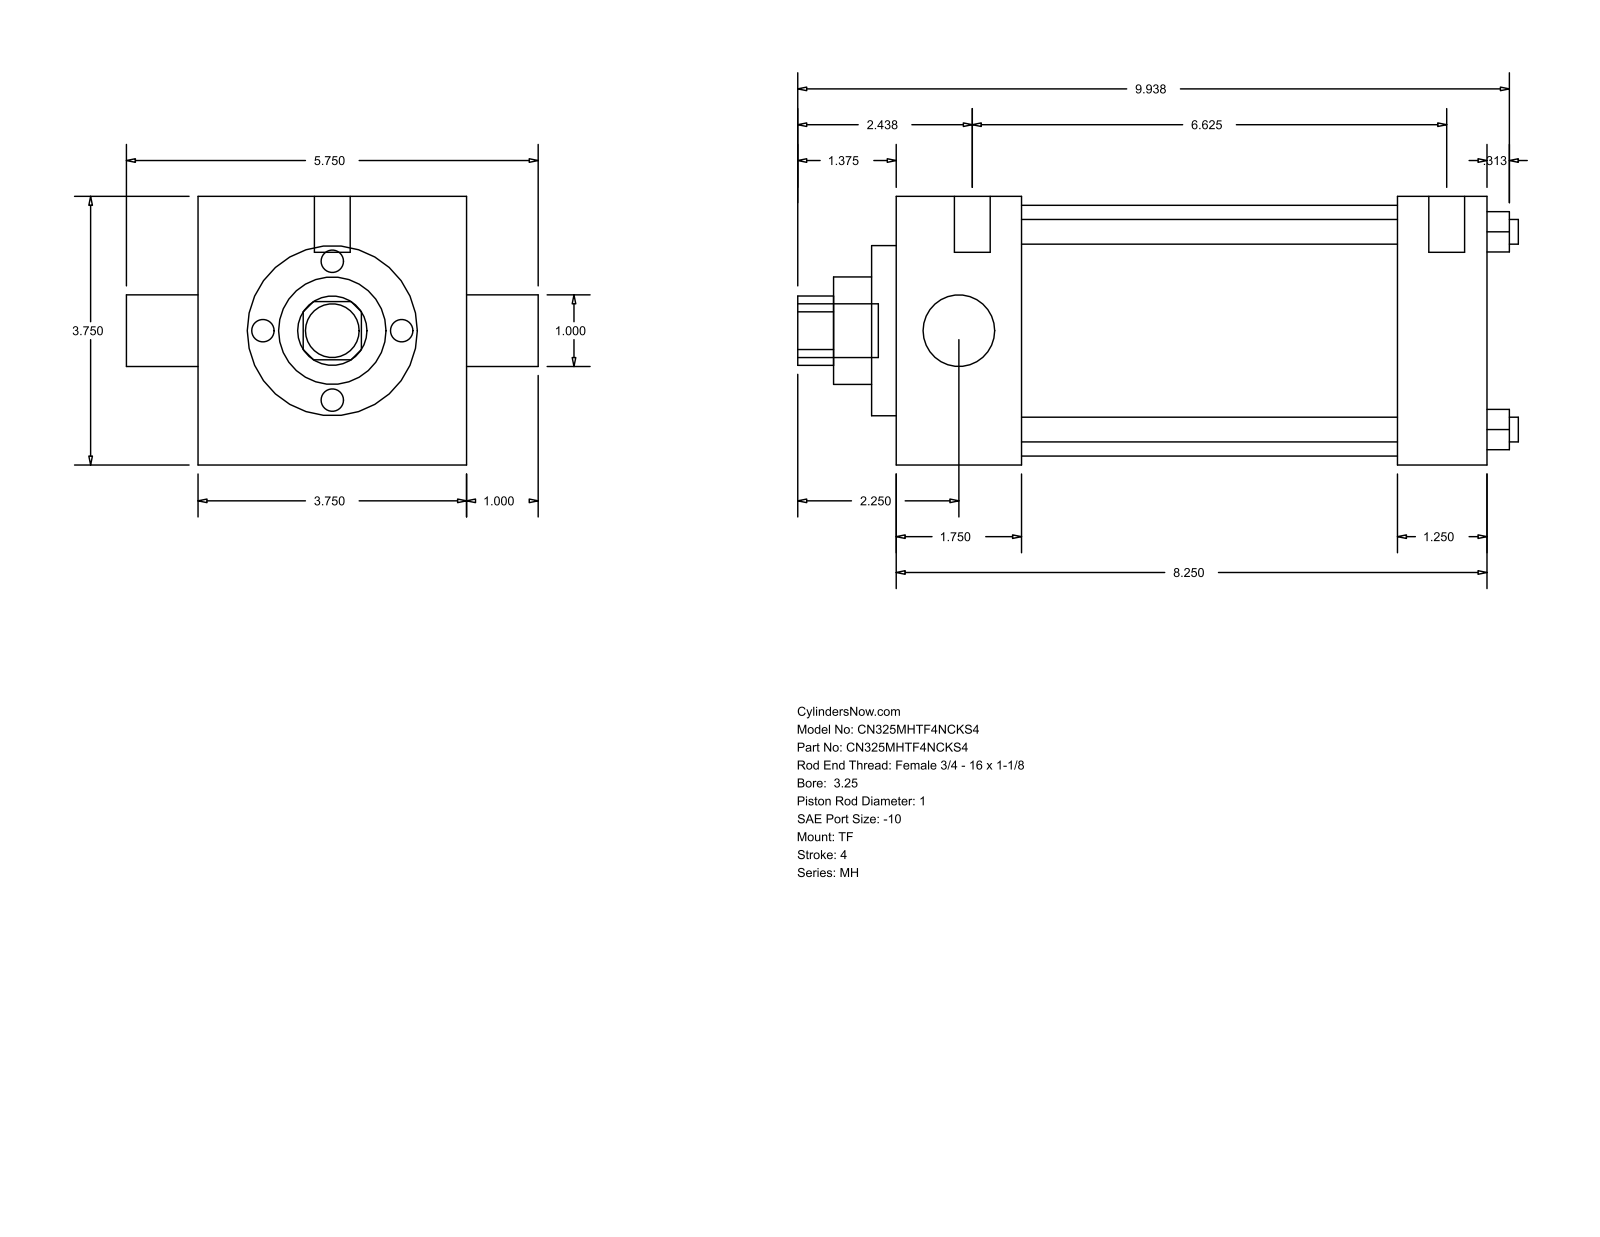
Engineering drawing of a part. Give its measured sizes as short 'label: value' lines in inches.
name: MH_TF__0325_1
written by: GSSL Pune (CONFIG_CONTROL_DESIGN)
unit: in
bodies: 0 solids, 86 faces (61 planar, 25 cylindrical, 0 other)
size: 10.063 × 5.75 × 3.75
holes: 4× ⌀0.345, 2× ⌀1, 1× ⌀1.5, 1× ⌀2.375, 1× ⌀3.5
bosses: 3× ⌀0.219, 2× ⌀0.5, 1× ⌀0.75
rounds: 1× R0.484
face distances: 3.75, 8.25, 1.75, 7, 5.25, 6.5, 1.25, 0.344, 2.094, 7.344
hole spacings: 1.952, 2.76, 3.903
